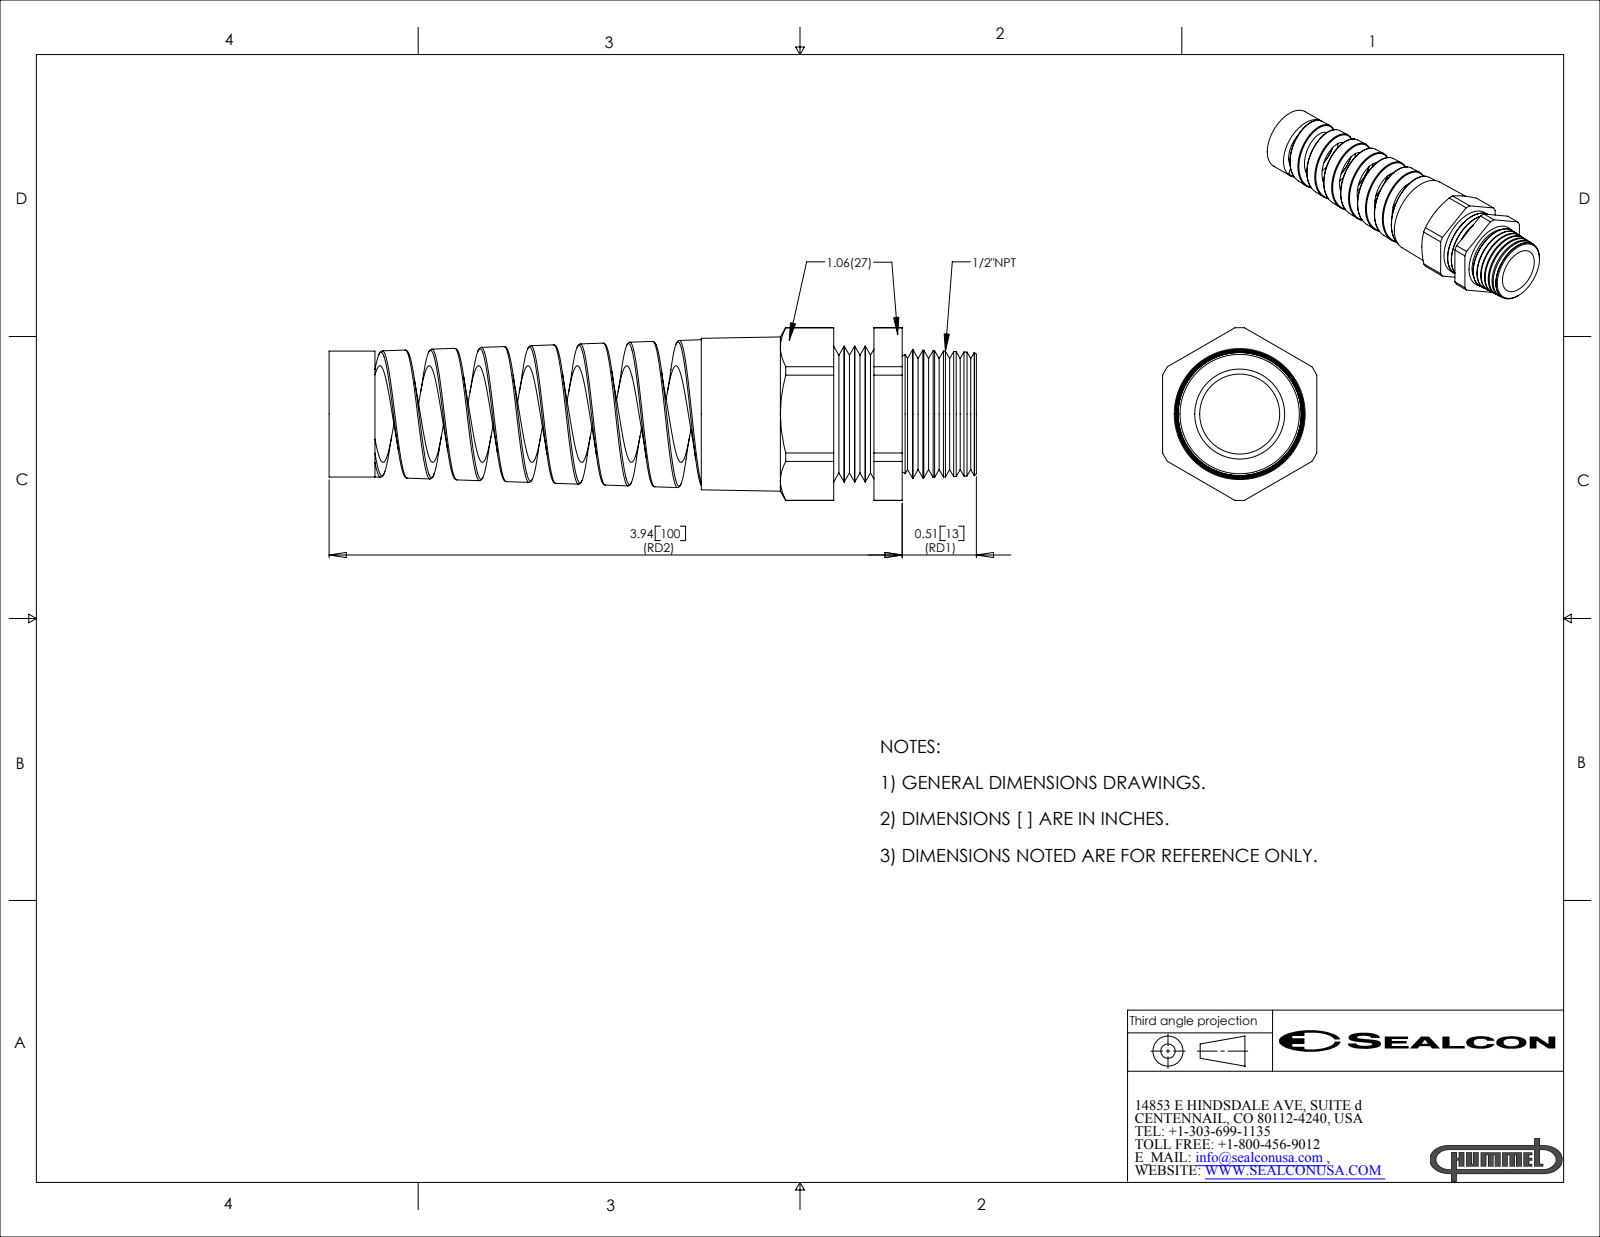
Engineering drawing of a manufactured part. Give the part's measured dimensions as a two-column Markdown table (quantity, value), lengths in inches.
| quantity | value |
| --- | --- |
| part name | CF16NA-BK |
| STEP written by | SolidWorks 2007 (CONFIG_CONTROL_DESIGN) |
| units | inches |
| bodies | 1 solid, 153 faces (19 planar, 39 cylindrical, 95 other) |
| overall size | 4.45 × 1.187 × 1.06 |
| volume | 1.469 in³ |
| surface area | 25.5 in² |
| round holes (diameter × count) | 0.55 × 1, 0.665 × 1 |
| round bosses / shafts (diameter × count) | 0.933 × 1, 0.865 × 1 |
| partial cylindrical surfaces (radius × count) | 0.594 × 1 |
| main face-to-face distances | 1.06, 1.381, 0.91, 0.471, 1.187, 0.277, 0.194, 2.559, 3.469, 3.746 |
